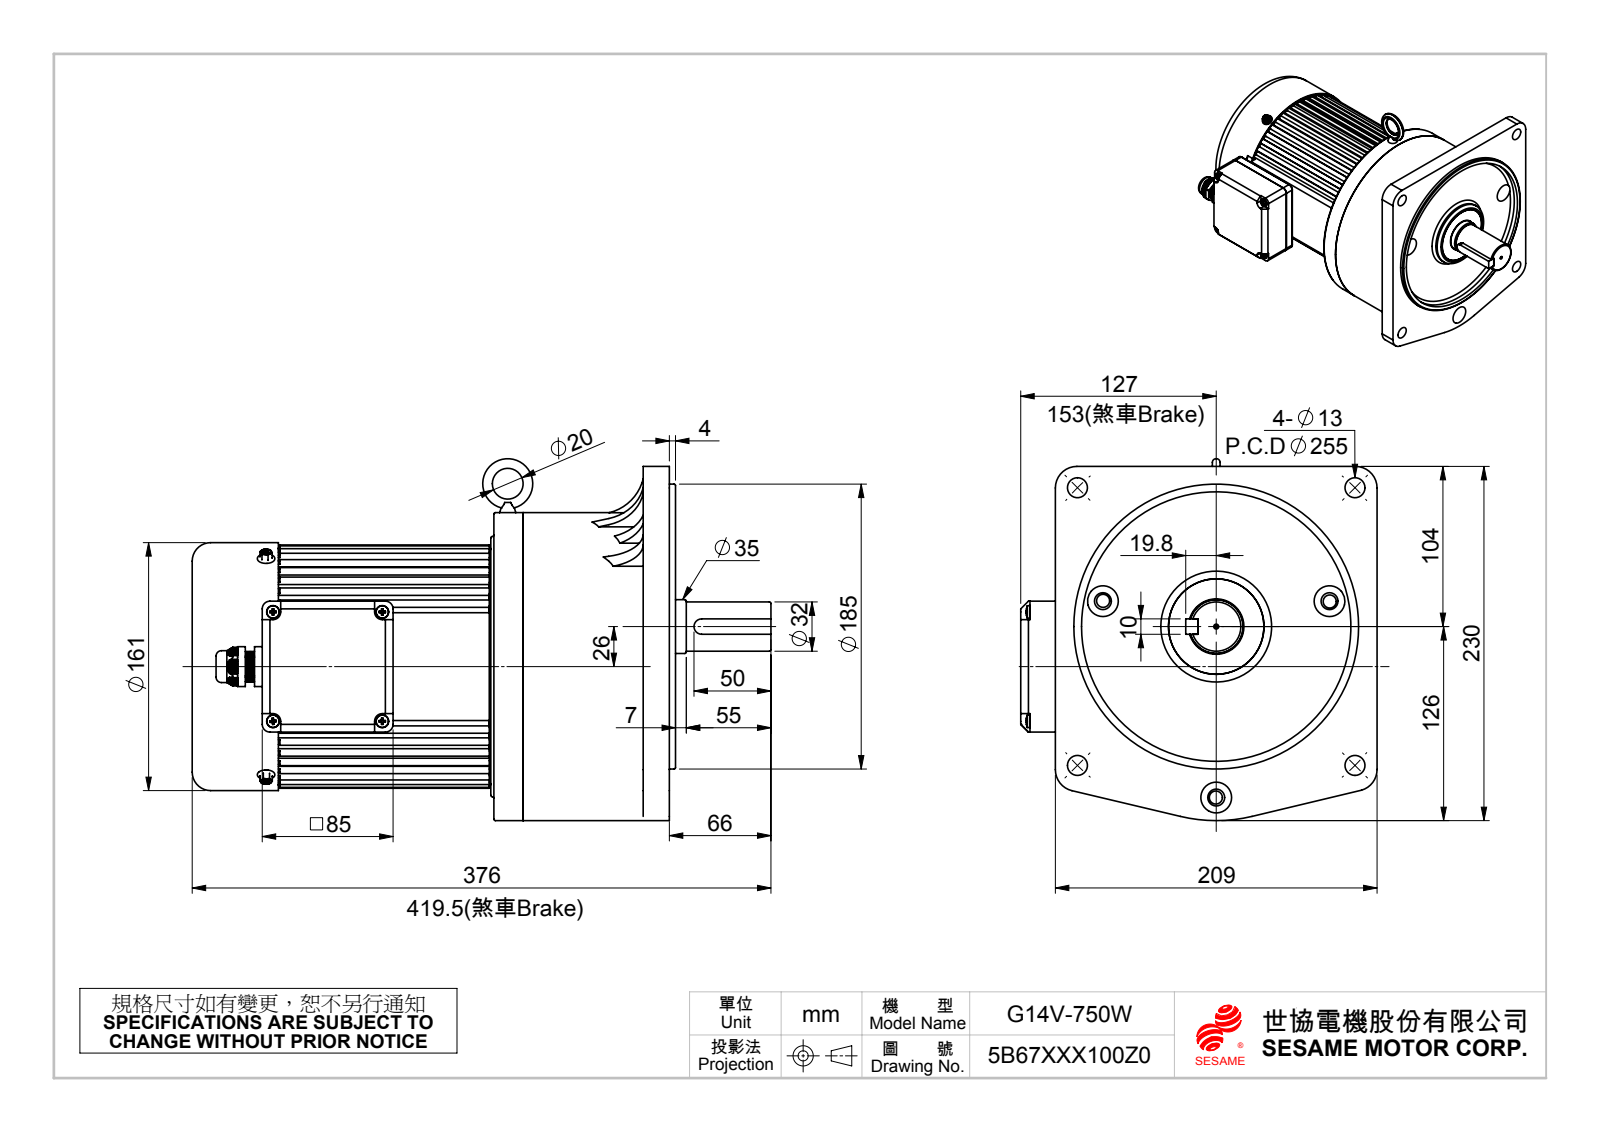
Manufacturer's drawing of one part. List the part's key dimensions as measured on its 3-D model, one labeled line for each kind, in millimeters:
Part name (STEP PRODUCT): 成品-塑膠T盒; 外六角內十字螺絲M5 x 10_ISO 4162 - M5 x 10 x 10-N; 10x8xL_50L; 750W風扇蓋159＊56 (+8 more)
STEP written by: SolidWorks 2010 (CONFIG_CONTROL_DESIGN)
Units: millimetres
Bodies: 20 solids, 3088 faces (1041 planar, 984 cylindrical, 1063 other)
Overall size (bounding box): 376 × 235 × 231.5
Volume: 7 130 000 mm³ · Surface area: 652 670 mm²
Round holes (diameter × count): ⌀5 ×11, ⌀3.3 ×9, ⌀8 ×5, ⌀6 ×4, ⌀13 ×4, ⌀20 ×4, ⌀4.2 ×3, ⌀8.5 ×3, ⌀11 ×3, ⌀15 ×3, ⌀2 ×1, ⌀6.8 ×1
Round bosses / shafts (diameter × count): ⌀8.3 ×4, ⌀4 ×4, ⌀5 ×3, ⌀200 ×1, ⌀185 ×1, ⌀161 ×1, ⌀159 ×1, ⌀150 ×1
Partial cylindrical surfaces — rounded edges, fillets, slot ends (radius × count): R2 ×75, R1 ×36, R3 ×18, R5 ×9, R30 ×8, R8 ×7, R0.5 ×6, R2.5 ×6
Main face-to-face distances: 4, 2, 27, 140, 167, 21.5, 117, 257, 90, 9.5
Hole centre spacings: 85, 147.22, 45, 64.77, 71, 127.51, 180.32, 147.1
